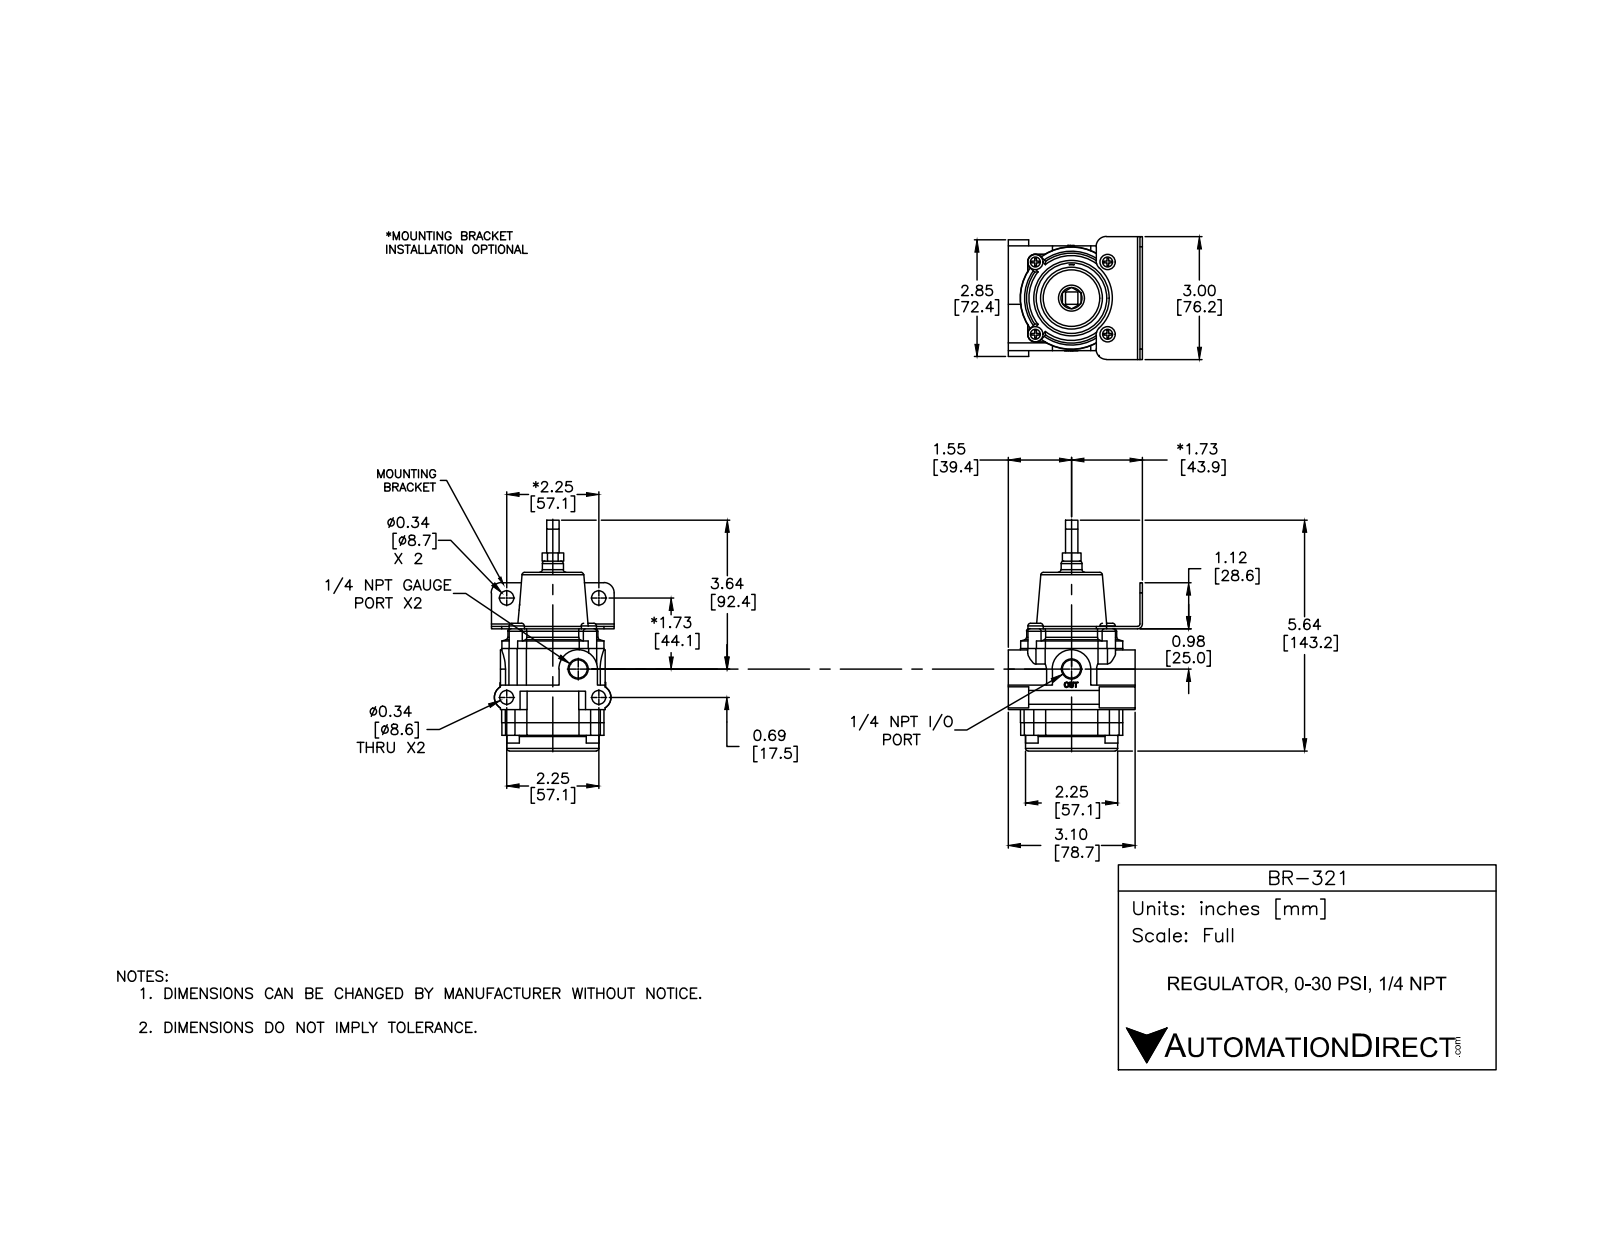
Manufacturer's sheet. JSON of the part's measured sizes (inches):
{"part_name": "BR-321", "step_written_by": "SolidWorks 2015 (CONFIG_CONTROL_DESIGN)", "units": "inches", "bodies": {"solids": 13, "faces": 1460, "planar": 268, "cylindrical": 963, "other": 229}, "overall_size": [5.613, 3.1, 2.85], "volume_in3": 18.6, "surface_area_in2": 96.84, "round_holes": [[0.159, 8], [0.201, 8], [0.34, 2], [0.438, 2], [0.257, 1]], "round_bosses_or_shafts": [[0.19, 8], [0.149, 8], [0.312, 5], [0.373, 4], [2.2, 1], [0.512, 1], [0.203, 1]], "partial_cylinders_radius": [[0.004, 48], [0.187, 8], [0.188, 8], [0.02, 6], [0.062, 4], [0.063, 3], [0.3, 2], [0.469, 2]], "face_to_face_distances": [1.81, 0.695, 2.505, 1.61, 0.915, 0.895, 0.385, 0.31, 1.225, 2.12], "hole_center_spacings": [1.858, 0.125, 1.944, 1.375, 1.25, 1.25, 1.768, 1.768]}
